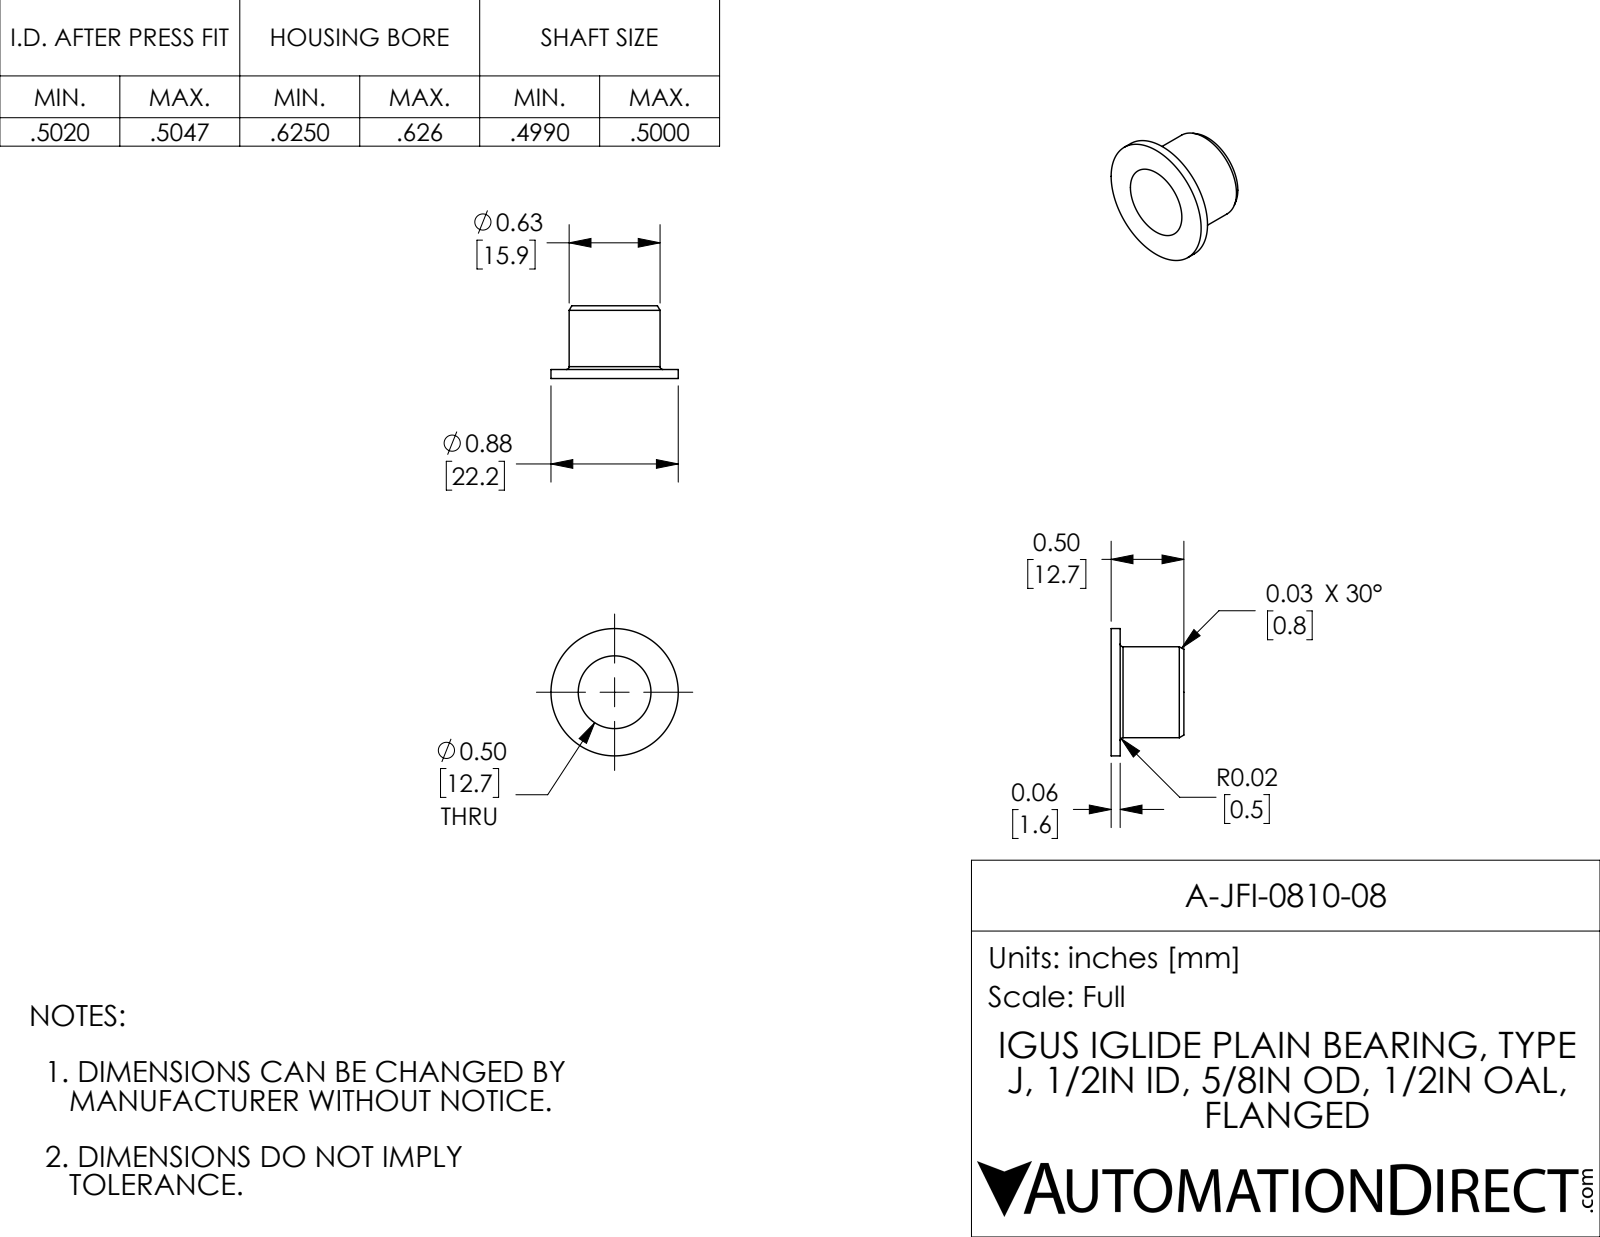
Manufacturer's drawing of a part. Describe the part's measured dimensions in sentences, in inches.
The part is named "A-JFI-0810-08". Its 3-D file was written by "SolidWorks 2017 (AUTOMOTIVE_DESIGN)". It is 1 solid with 13 faces: 3 planar, 6 cylindrical and 4 other. Overall it measures 0.875 by 0.875 by 0.5 inches. Its volume is 0.073 cubic inches and its surface area 2.582 square inches. Round holes: 1 of diameter 0.5. Round bosses or shafts: 1 of diameter 0.875, 1 of diameter 0.625. The main face-to-face distances are 0.062, 0.5, 0.438.
